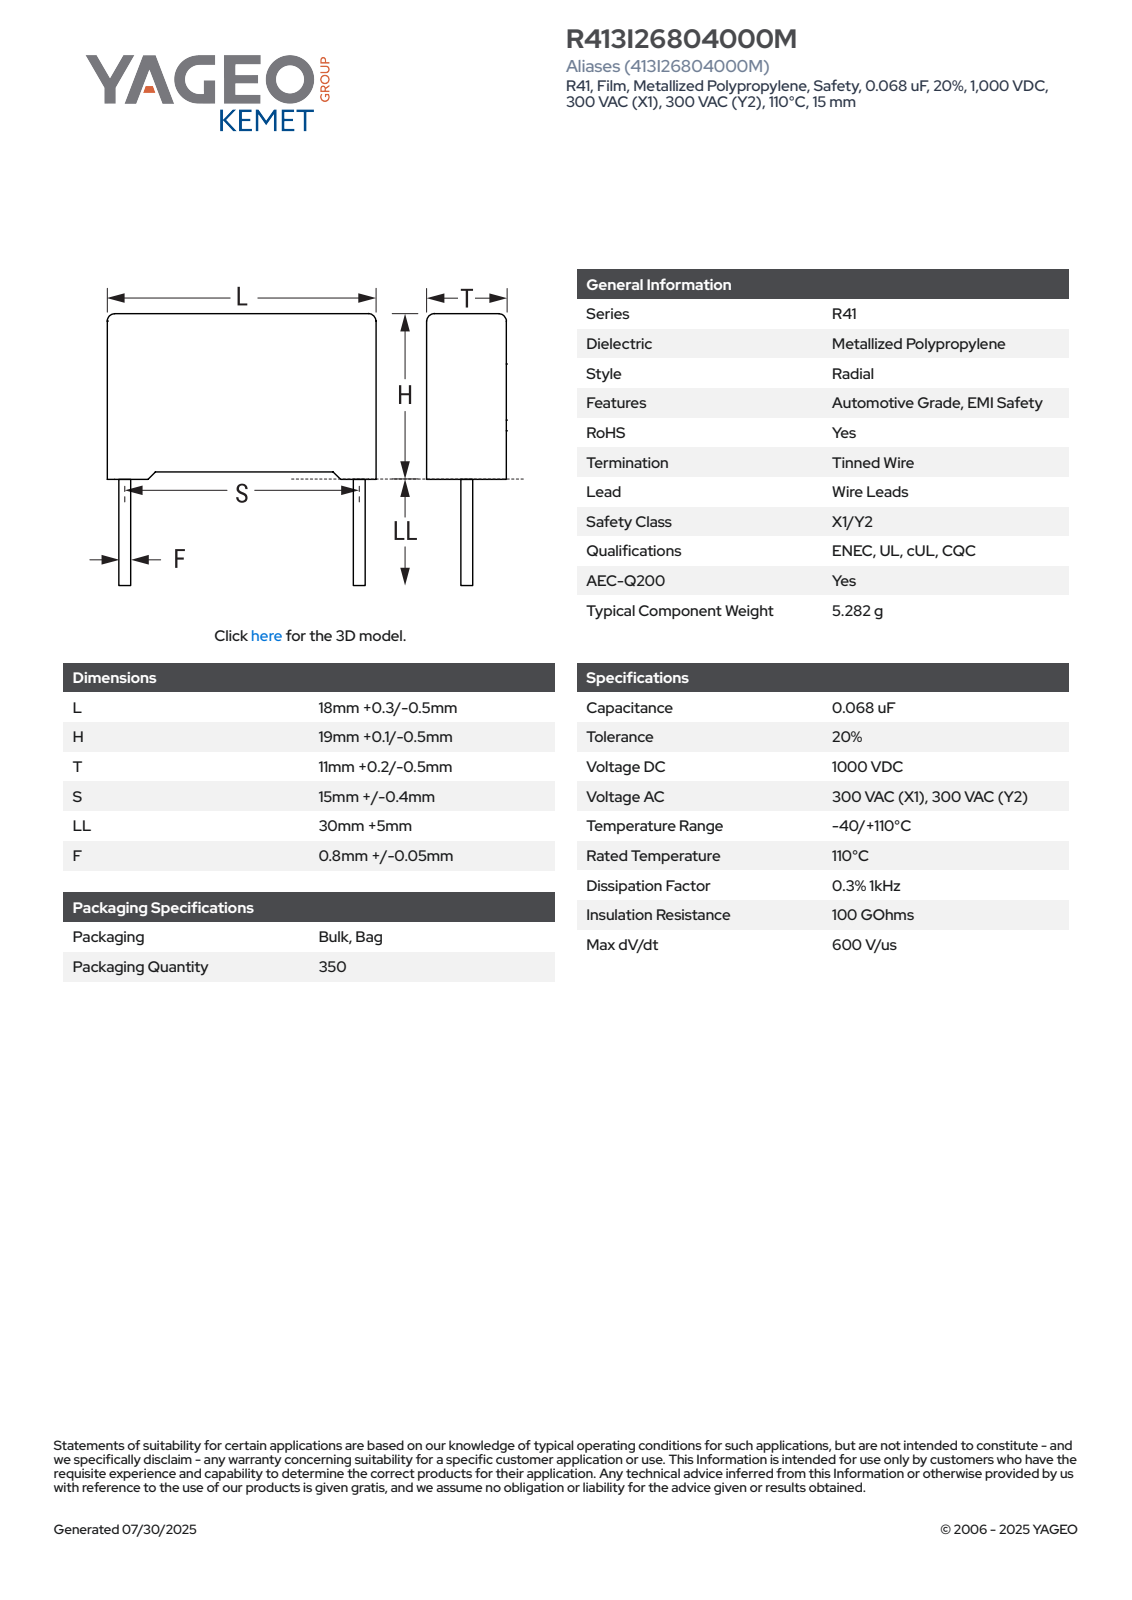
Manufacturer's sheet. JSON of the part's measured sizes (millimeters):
{"part_name": "CFR_RB2_18X19X11_L18.3H19.1T11.2S15LL35F0.85", "step_written_by": "SolidWorks 2021 (AUTOMOTIVE_DESIGN)", "units": "millimeters", "bodies": {"solids": 4, "faces": 85, "planar": 77, "cylindrical": 8, "other": 0}, "overall_size": [54.1, 18.3, 11.21], "volume_mm3": 3815, "surface_area_mm2": 1751, "round_bosses_or_shafts": [[0.85, 2]], "partial_cylinders_radius": [[0.5, 4]], "face_to_face_distances": [11.2, 18.3, 18.35, 0.61, 0.75, 19.1, 17.69, 0.66, 18.44, 10.59]}
